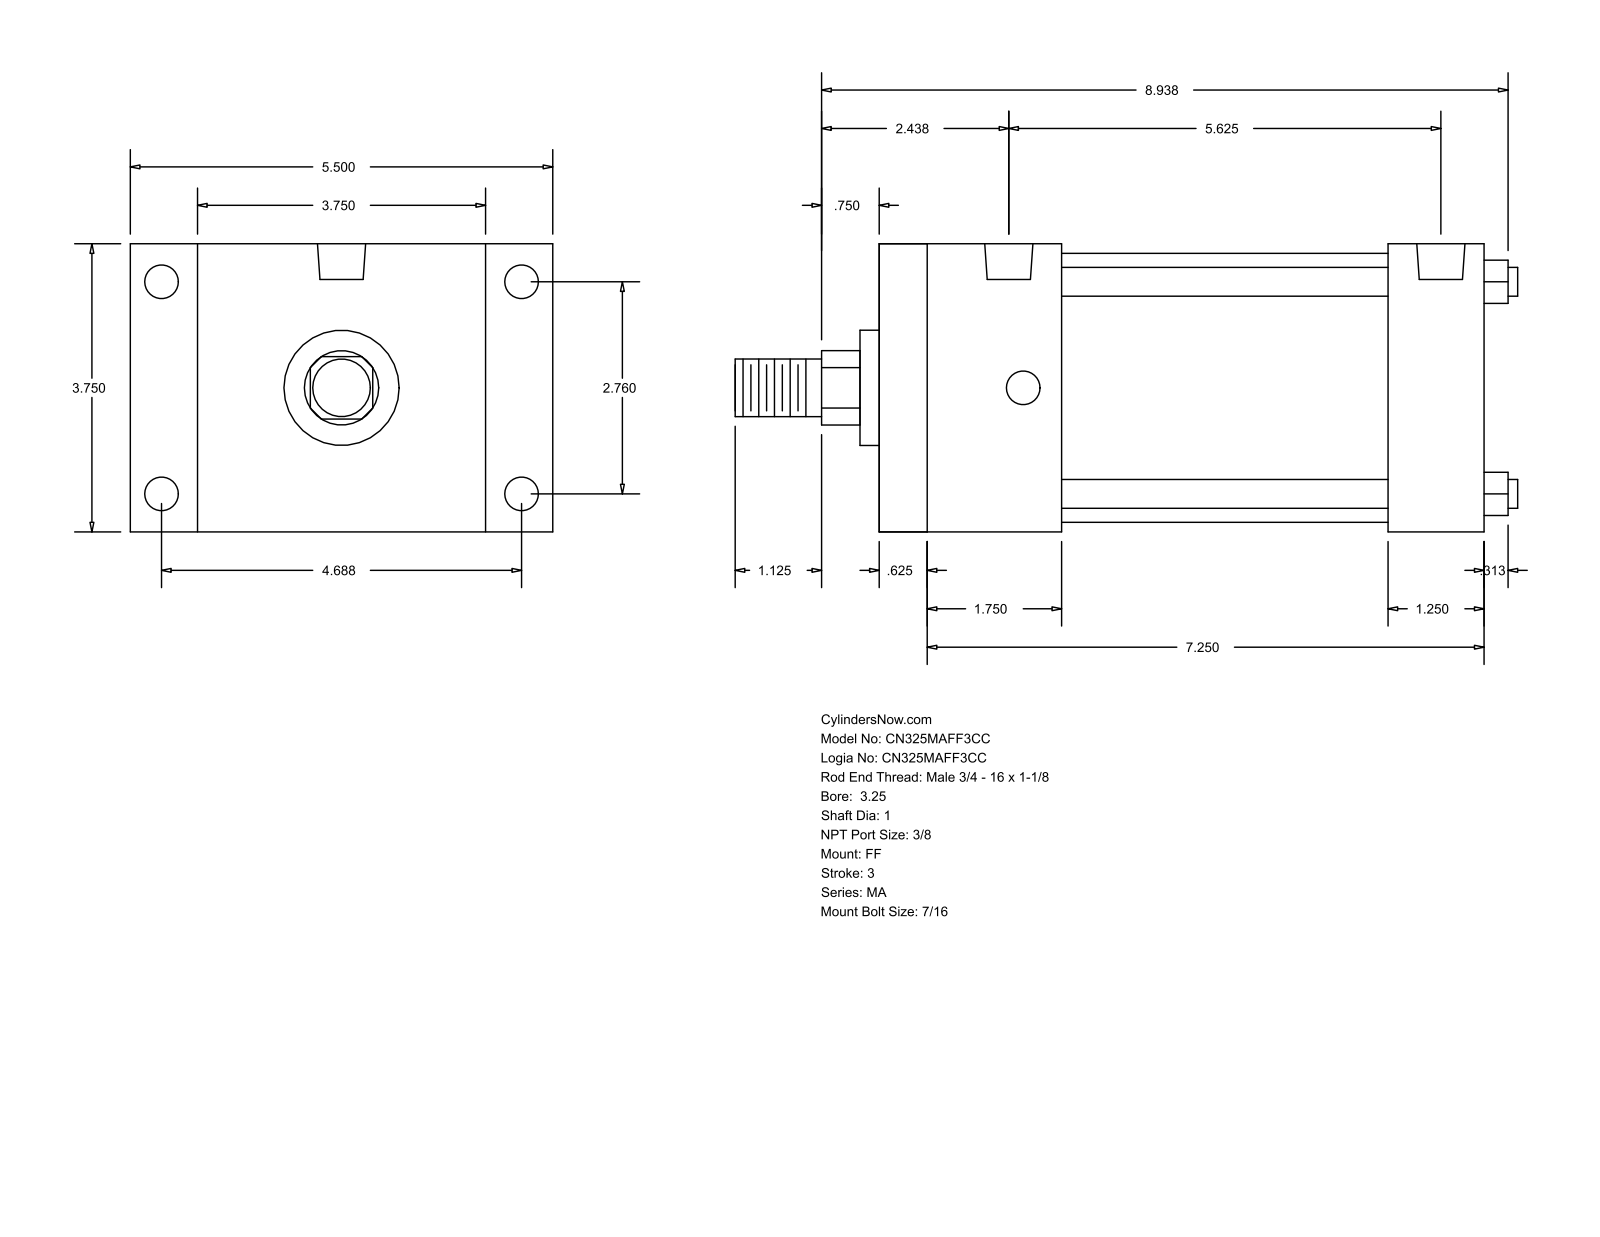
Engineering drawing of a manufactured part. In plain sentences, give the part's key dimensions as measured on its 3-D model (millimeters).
The part is named "MA_FF__0325_1". Its 3-D file was written by "GSSL Pune (CONFIG_CONTROL_DESIGN)". It is 0 solids with 92 faces: 64 planar, 28 cylindrical and 0 other. Overall it measures 258.76 by 139.7 by 95.25 millimeters. Round holes: 8 of diameter 11.11, 2 of diameter 15.93. Round bosses or shafts: 4 of diameter 9.53, 1 of diameter 88.9, 1 of diameter 38.1, 1 of diameter 25.4, 1 of diameter 19.05. Partial cylindrical surfaces (rounded edges, fillets, slot ends): 1 of radius 12.29. The main face-to-face distances are 95.24, 200.02, 15.87, 184.15, 22.23, 117.47, 60.33, 168.27, 44.46, 152.4. The hole center spacings are 4.76, 70.1, 119.06, 133.36, 138.12, 138.16, 142.88.
